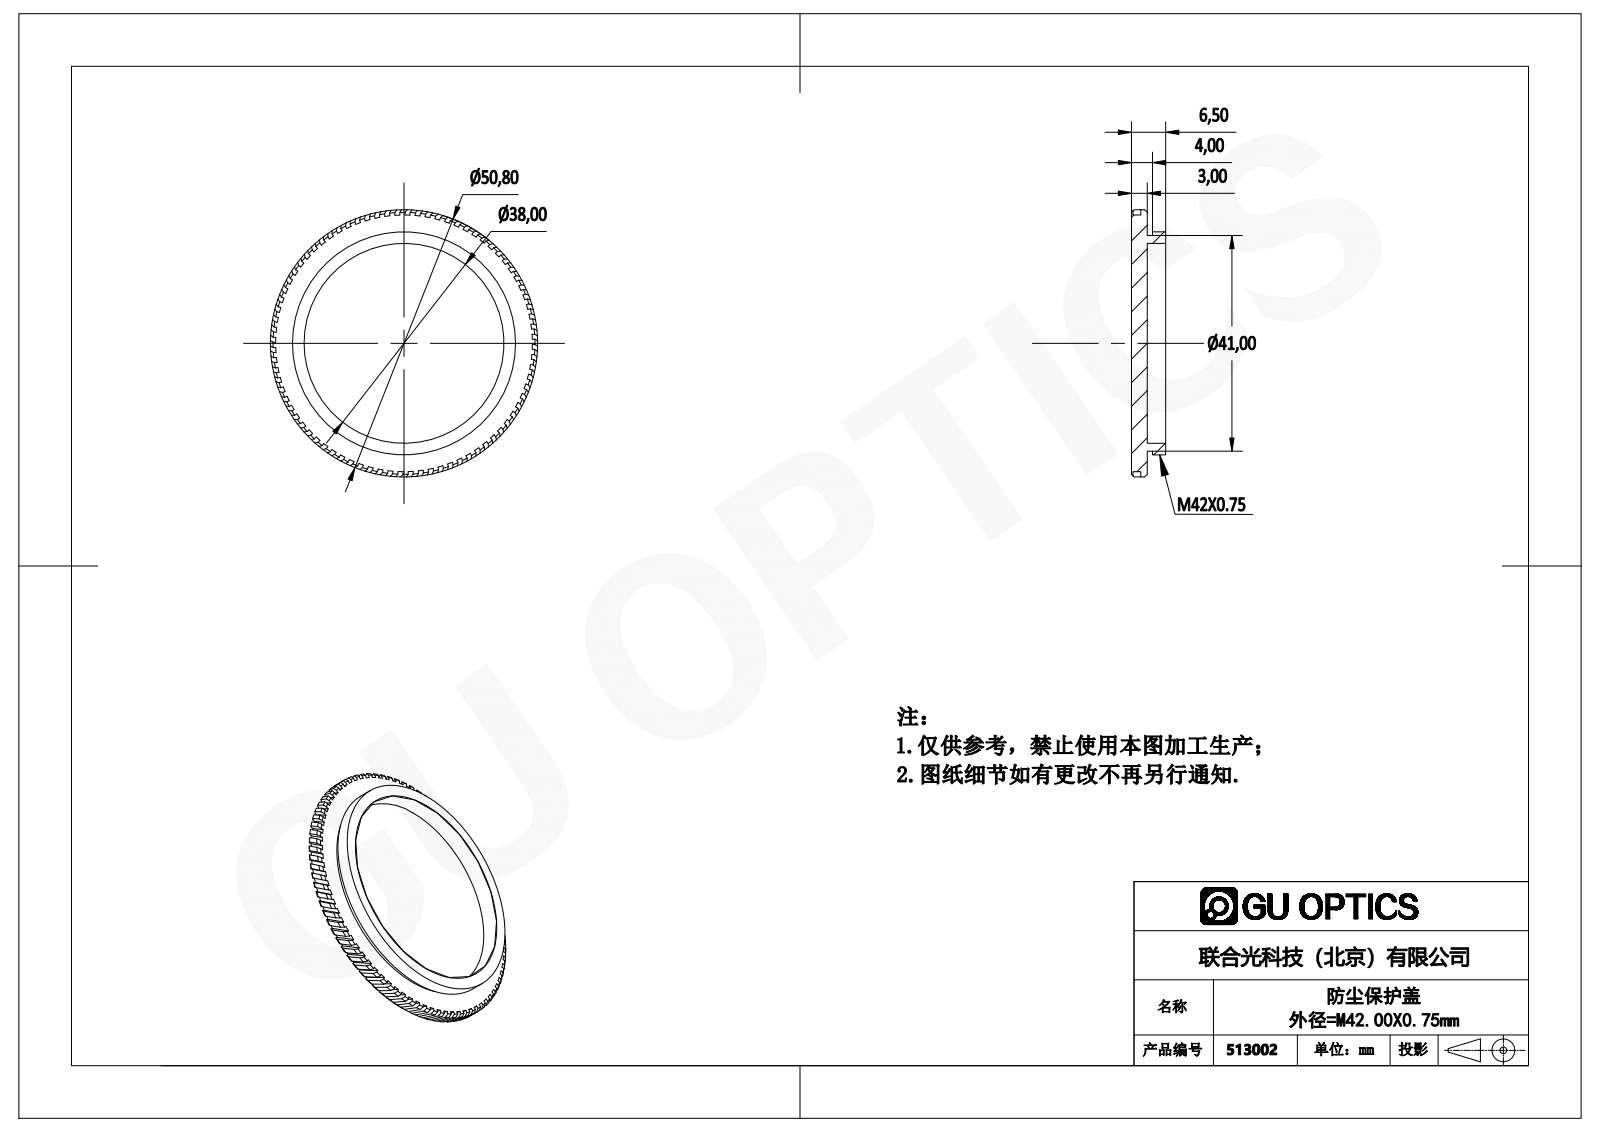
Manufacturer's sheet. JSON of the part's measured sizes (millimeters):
{"part_name": "513002", "step_written_by": "SolidWorks 2016 (AUTOMOTIVE_DESIGN)", "units": "millimeters", "bodies": {"solids": 1, "faces": 574, "planar": 165, "cylindrical": 247, "other": 162}, "overall_size": [50.8, 50.8, 6.5], "volume_mm3": 7867, "surface_area_mm2": 5851, "round_holes": [[32, 1]], "round_bosses_or_shafts": [[50.8, 1], [48.8, 1], [42.4, 1], [41, 1]], "face_to_face_distances": [3, 3.5, 6.5, 0.8, 2.5, 1, 4, 0.81]}
